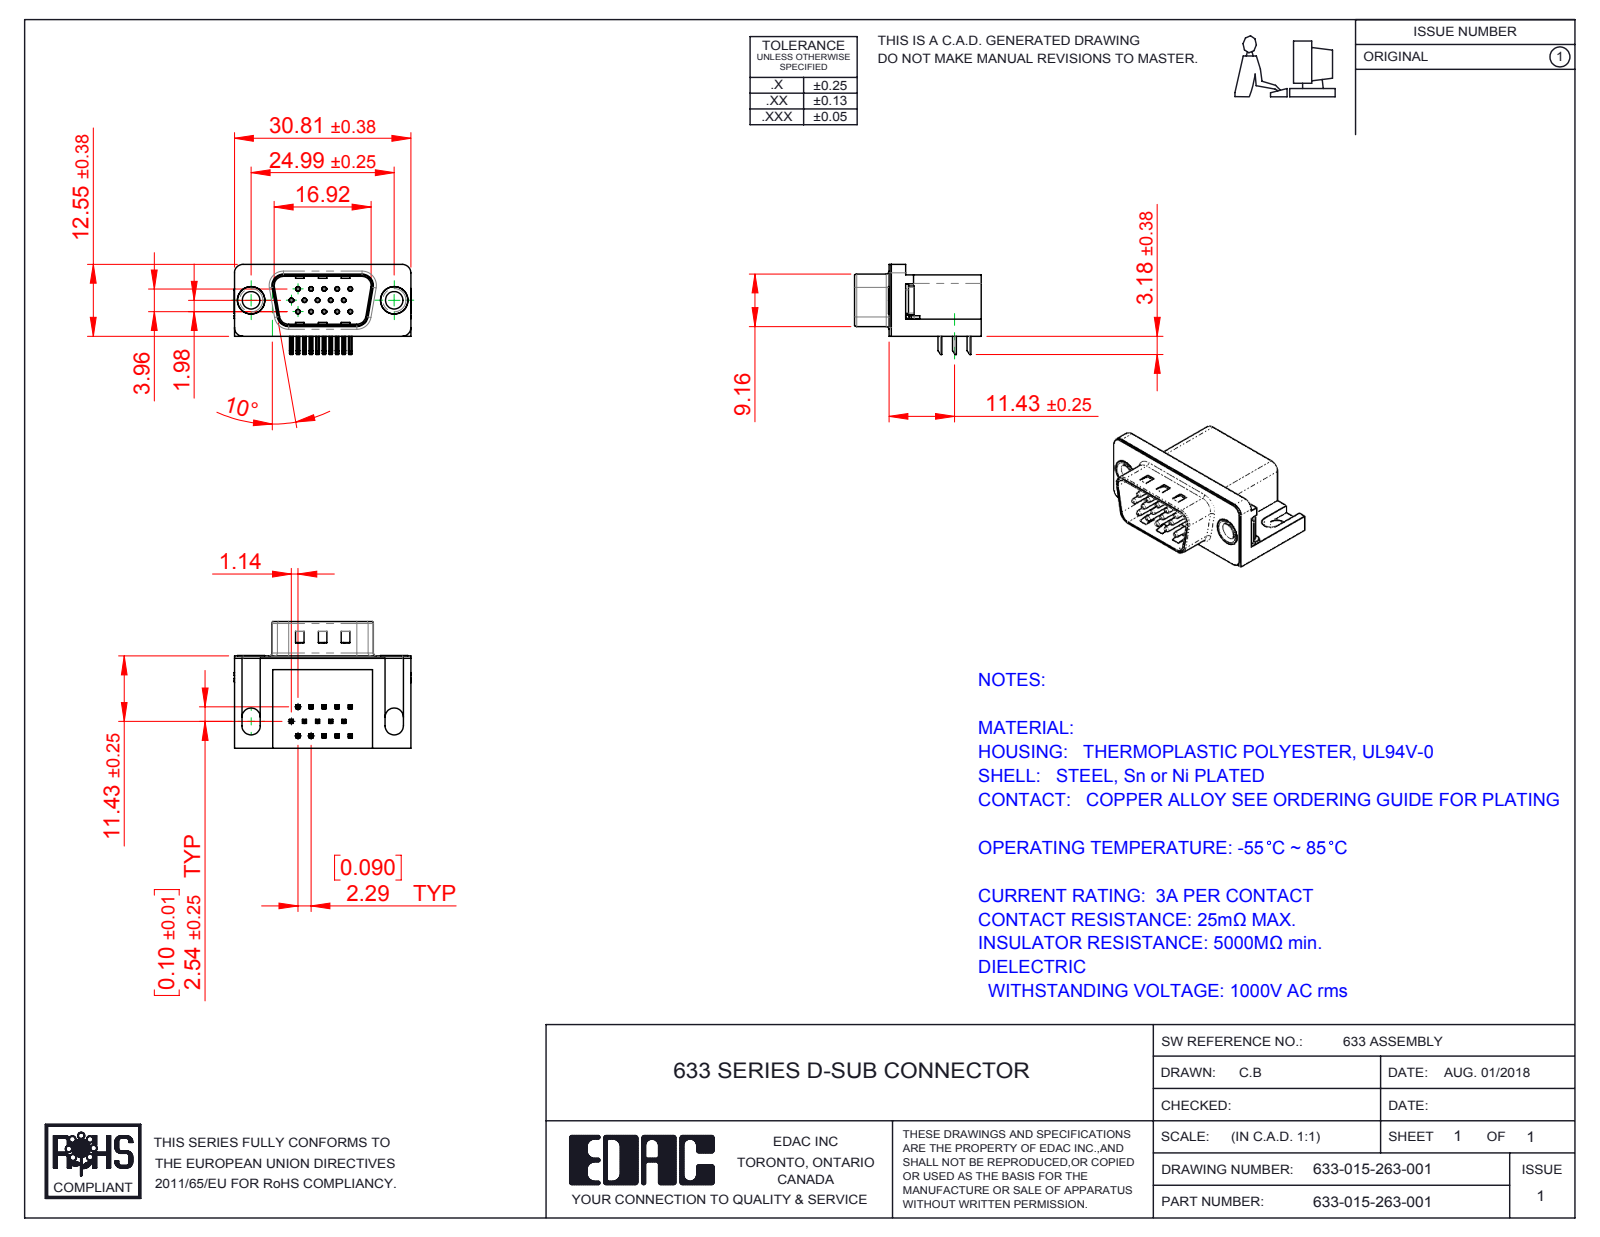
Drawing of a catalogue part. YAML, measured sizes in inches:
part_name: "633 Non Board Mount; 633 Housing_15 Contact; 633 Thru Hole Rivet; 633 Contact Middle (+4 more)"
step_written_by: "SolidWorks 2016 (CONFIG_CONTROL_DESIGN)"
units: inches
bodies: {solids: 21, faces: 1399, planar: 861, cylindrical: 421, other: 117}
overall_size: [1.216, 0.87, 0.619]
volume: 0.245
surface_area: 8.034
round_holes:
  - {diameter: 0.014, count: 15}
  - {diameter: 0.031, count: 15}
  - {diameter: 0.12, count: 2}
  - {diameter: 0.157, count: 2}
  - {diameter: 0.189, count: 2}
  - {diameter: 0.197, count: 2}
round_bosses_or_shafts:
  - {diameter: 0.03, count: 15}
  - {diameter: 0.193, count: 2}
  - {diameter: 0.187, count: 2}
  - {diameter: 0.152, count: 2}
partial_cylinders:
  - {radius: 0.01, count: 68}
  - {radius: 0.005, count: 30}
  - {radius: 0.039, count: 16}
  - {radius: 0.02, count: 9}
  - {radius: 0.063, count: 8}
  - {radius: 0.059, count: 7}
  - {radius: 0.035, count: 4}
  - {radius: 0.079, count: 4}
face_to_face_distances: [0.016, 0.407, 0.618, 0.114, 0.098, 0.264, 0.634, 0.014, 0.421, 0.52]
hole_center_spacings: [0.156, 0.09, 0.18, 0.09, 0.238, 0.27, 0.312, 0.238]
